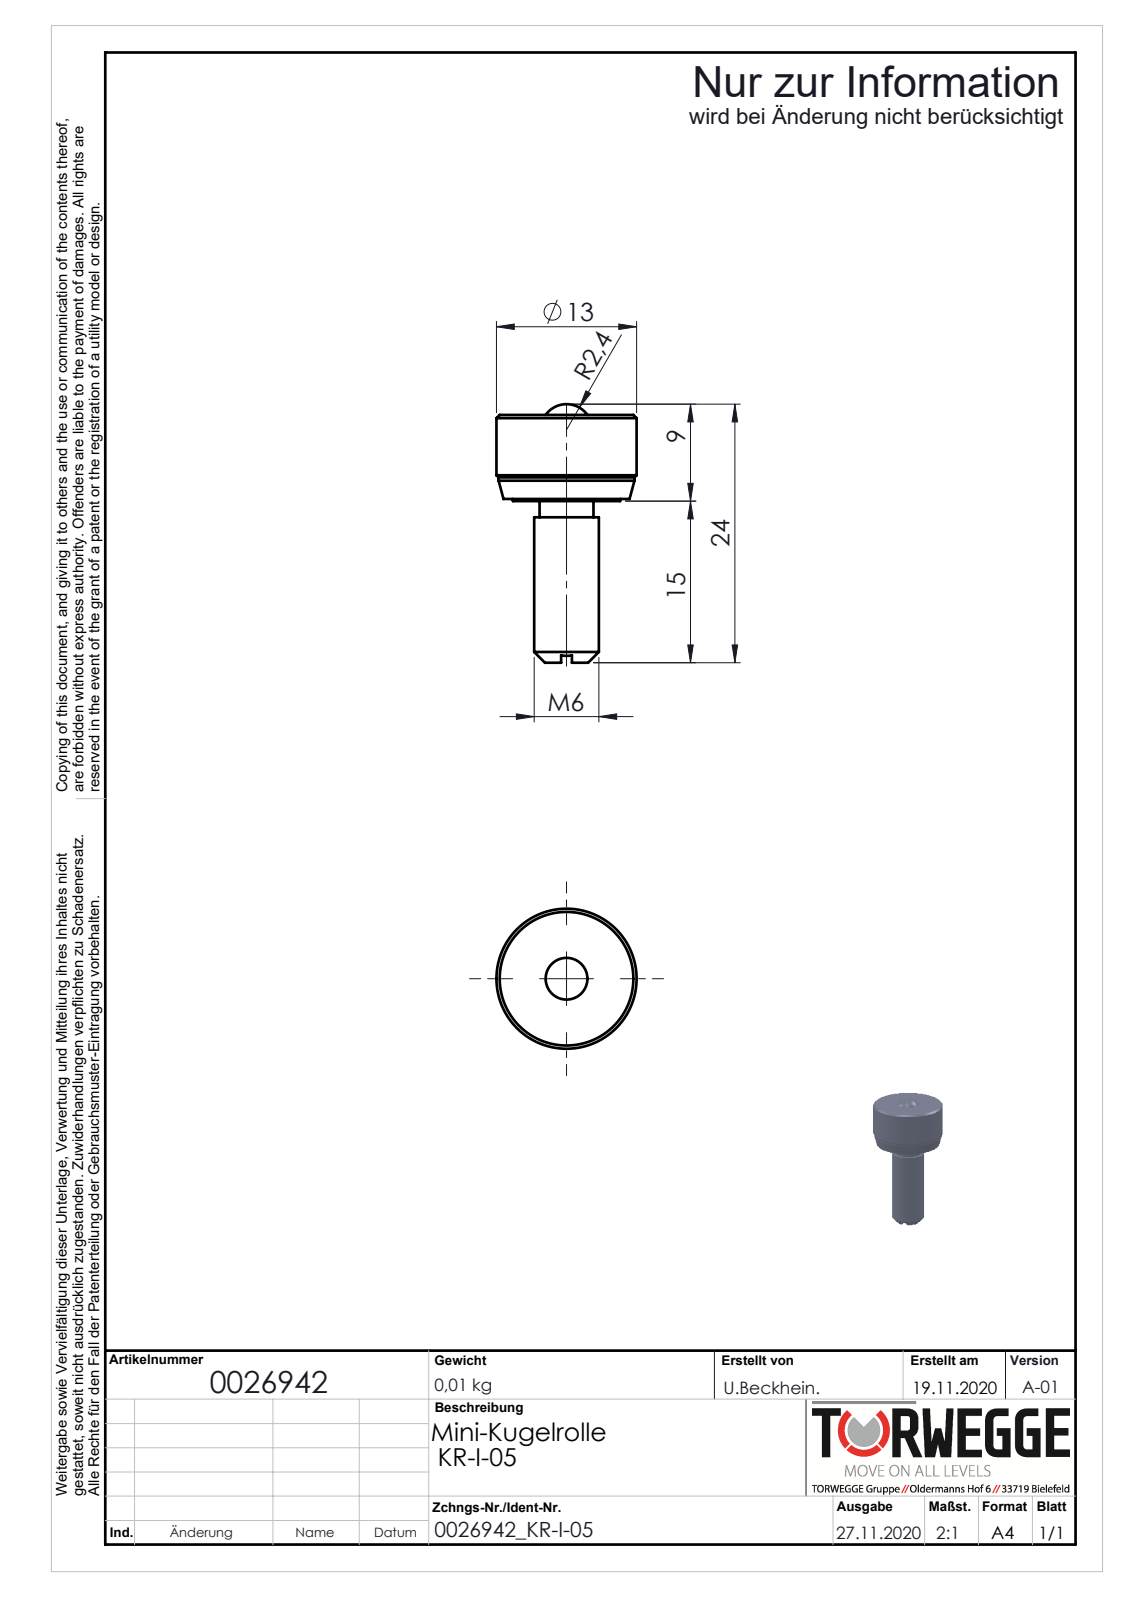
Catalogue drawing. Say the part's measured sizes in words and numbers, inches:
The part is named "0026942". Its 3-D file was written by "SolidWorks 2018 (AUTOMOTIVE_DESIGN)". It is 1 solid with 30 faces: 11 planar, 8 cylindrical and 11 other. Overall it measures 0.945 by 0.512 by 0.512 inches. Its volume is 0.087 cubic inches and its surface area 1.32 square inches. Round bosses or shafts: 1 of diameter 0.512, 1 of diameter 0.496, 1 of diameter 0.236, 1 of diameter 0.197. The main face-to-face distances are 0.315, 0.307, 0.039, 0.059, 0.067, 0.374, 0.531, 0.591, 0.598, 0.906.
